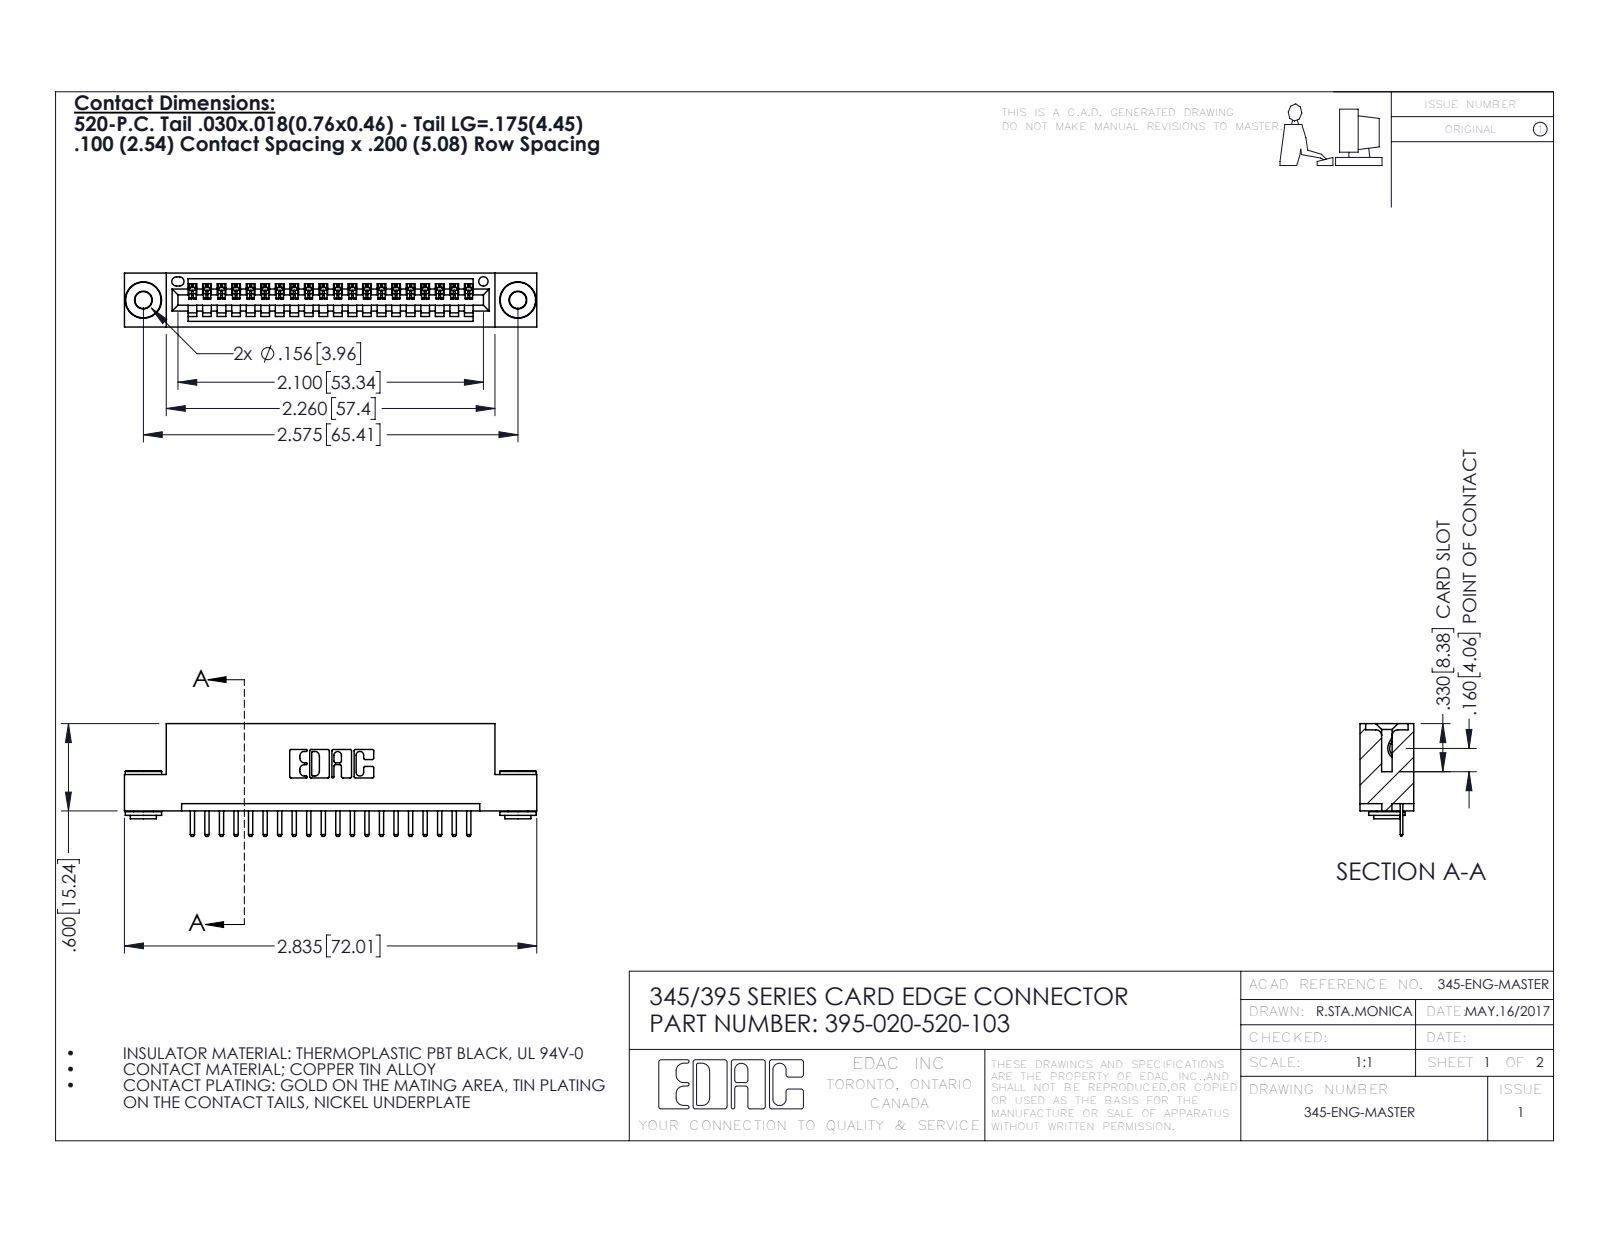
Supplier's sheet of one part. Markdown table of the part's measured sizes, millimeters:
| quantity | value |
| --- | --- |
| part name | 395-020-520-103; 345-250-002_345-250-002-102; 345-292-001_345-293-120; 345 Part_Flush Mounting Lugs - 0.156 Dia-TH |
| STEP written by | SolidWorks 2016 (CONFIG_CONTROL_DESIGN) |
| units | millimeters |
| bodies | 23 solids, 1404 faces (930 planar, 466 cylindrical, 8 other) |
| overall size | 72 × 19.7 × 9.4 |
| volume | 6 620 mm³ |
| surface area | 8 529 mm² |
| round holes (diameter × count) | 2.9 × 2, 4 × 2, 1.6 × 1 |
| round bosses / shafts (diameter × count) | 6.4 × 2, 4.6 × 2, 3.5 × 2 |
| partial cylindrical surfaces (radius × count) | 0.3 × 42, 0.2 × 40, 0.3 × 22, 0.2 × 6, 0.8 × 6, 0.7 × 3, 0.8 × 2, 1 × 2 |
| main face-to-face distances | 1.8, 7.6, 5.1, 9.4, 0.6, 2.5, 6.9, 5.7, 1.8, 3.8 |
| hole center spacings | 6.9, 59.5, 65.4 |
